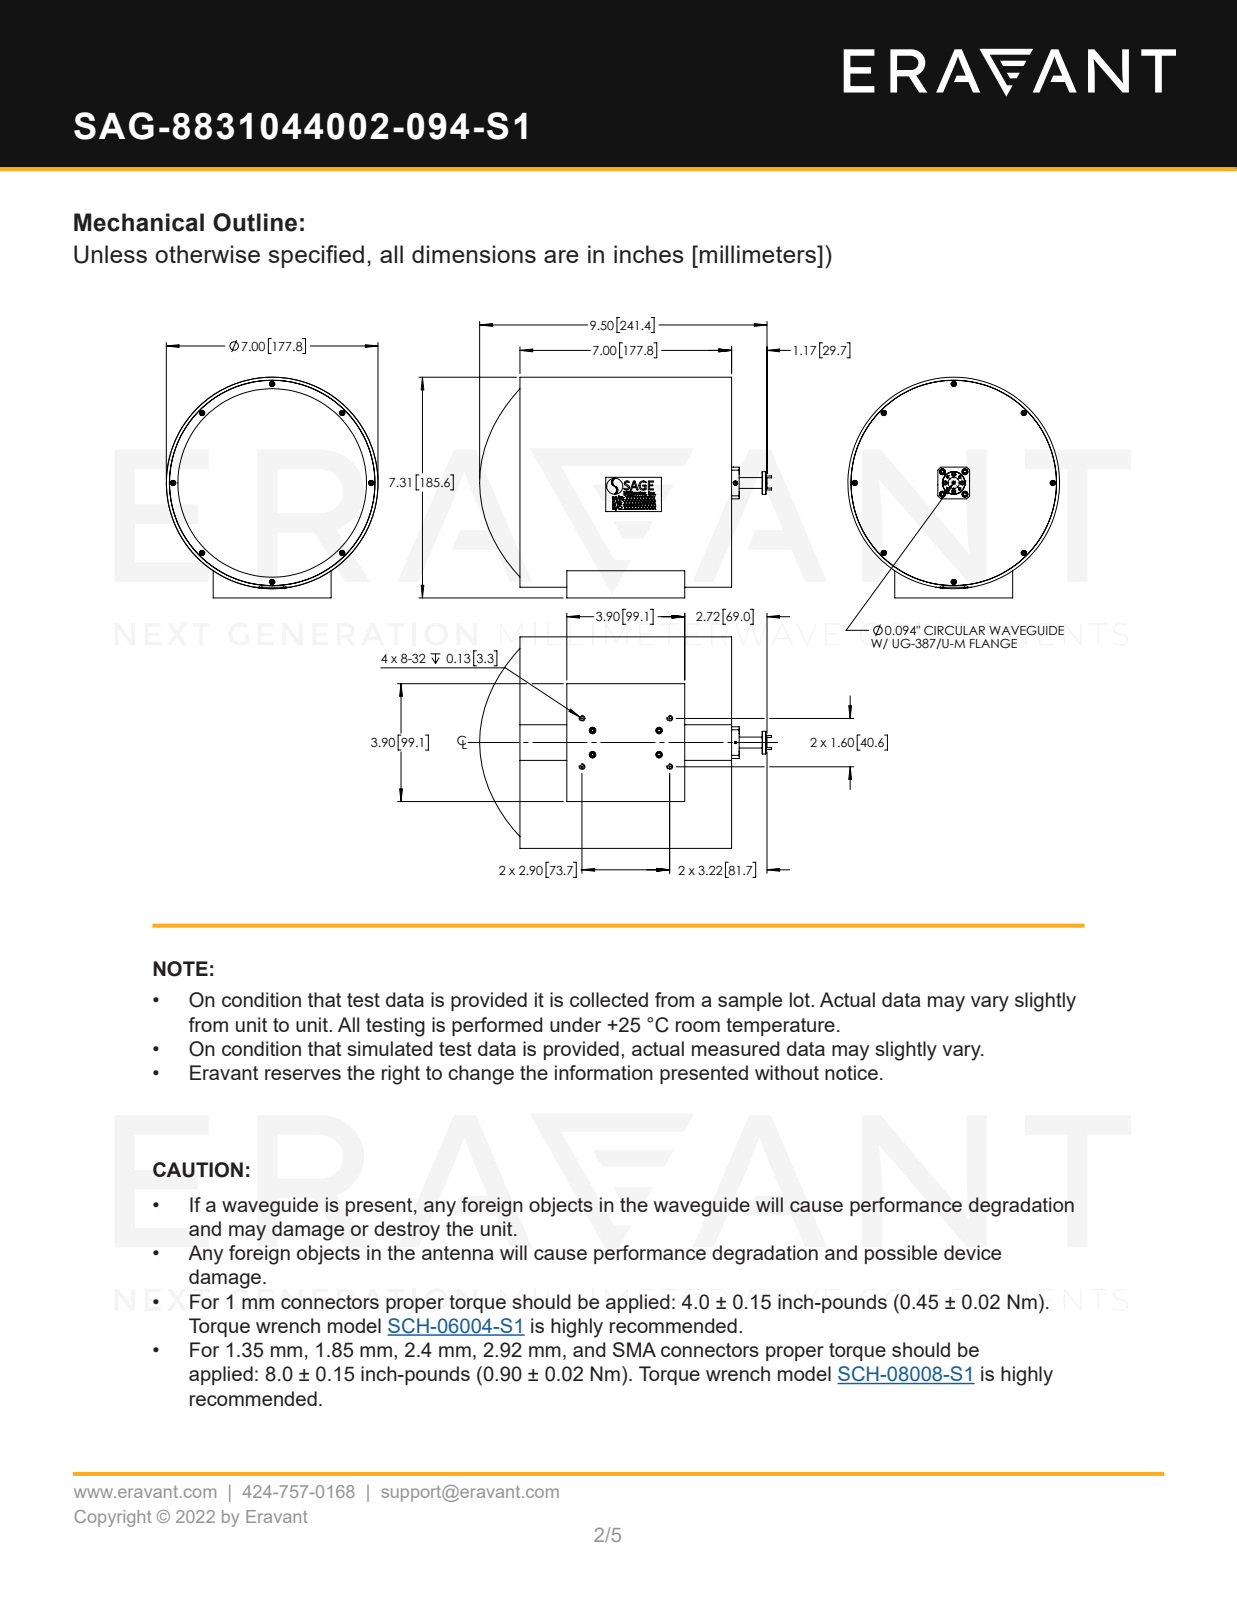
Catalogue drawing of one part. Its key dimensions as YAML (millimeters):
part_name: "SAG-8831044002-094-S1"
step_written_by: "SolidWorks 2020 (CONFIG_CONTROL_DESIGN)"
units: millimeters
bodies: {solids: 47, faces: 1168, planar: 499, cylindrical: 365, other: 304}
overall_size: [245.3, 185.6, 177.8]
volume: 1489000
surface_area: 335000
round_holes:
  - {diameter: 2.3, count: 12}
  - {diameter: 1.8, count: 8}
  - {diameter: 2.5, count: 8}
  - {diameter: 3, count: 8}
  - {diameter: 3.3, count: 8}
  - {diameter: 3.5, count: 6}
  - {diameter: 3.6, count: 4}
  - {diameter: 5.2, count: 4}
  - {diameter: 5.6, count: 4}
  - {diameter: 1.5, count: 3}
  - {diameter: 1.7, count: 2}
  - {diameter: 2.4, count: 1}
round_bosses_or_shafts:
  - {diameter: 4.6, count: 8}
  - {diameter: 4.6, count: 8}
  - {diameter: 2.8, count: 8}
  - {diameter: 2.2, count: 8}
  - {diameter: 1.6, count: 3}
  - {diameter: 4.2, count: 2}
  - {diameter: 177.8, count: 1}
  - {diameter: 172.5, count: 1}
partial_cylinders:
  - {radius: 1.4, count: 8}
  - {radius: 17.1, count: 1}
face_to_face_distances: [171.5, 174.6, 3.2, 9, 3.2, 174.6, 177.8, 99.1, 39.4, 138.4]
hole_center_spacings: [83.5, 88.4, 5.5, 9.7, 15.1, 19.1, 76, 78.3]
